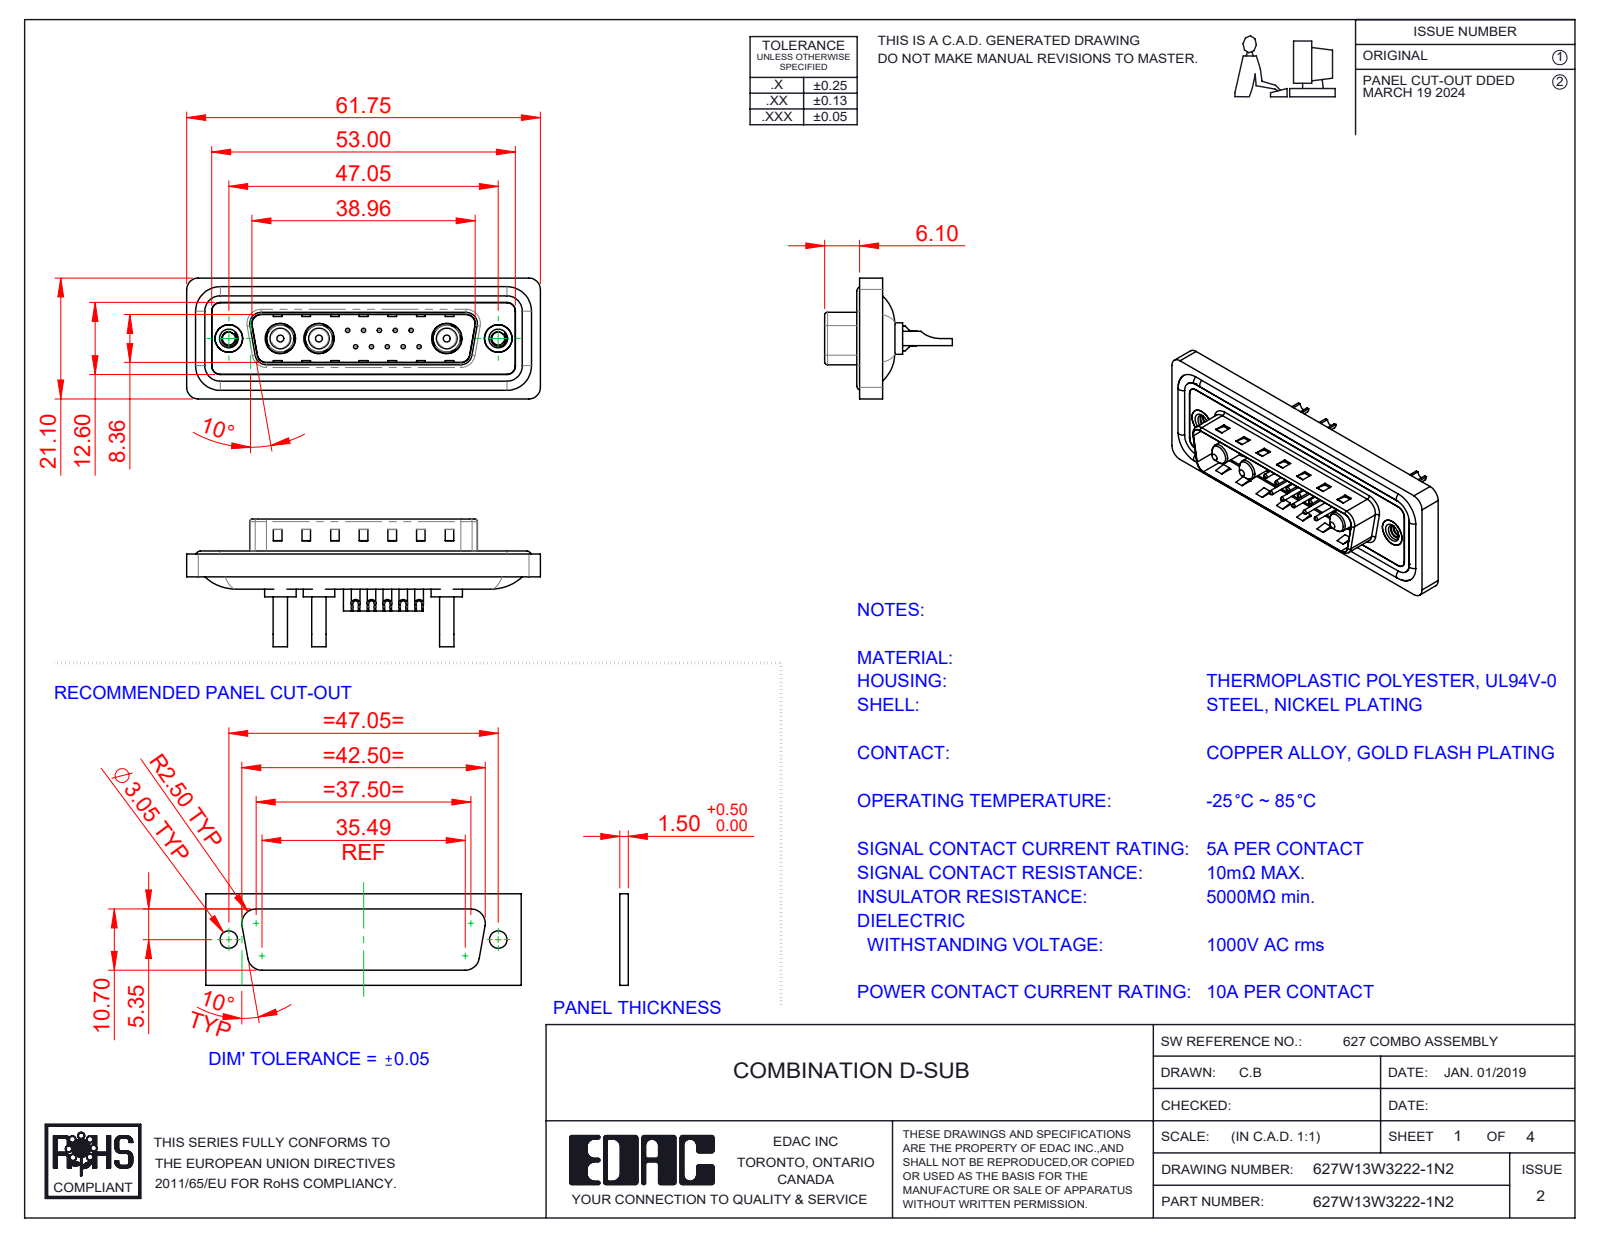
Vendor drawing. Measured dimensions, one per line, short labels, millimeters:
name: 627Combo Contact Row 2_22; 627Combo Shell Front_25 Contacts; 627Combo Waterproof Housing_25 Contacts; Power Pin_10A SC (+5 more)
written by: SolidWorks 2023 (CONFIG_CONTROL_DESIGN)
unit: mm
bodies: 23 solids, 988 faces (335 planar, 414 cylindrical, 239 other)
size: 61.75 × 22.3 × 21.1
volume: 7 342 mm³; area: 12 097 mm²
holes: 10× ⌀0.75, 10× ⌀1, 10× ⌀1.6, 10× ⌀2, 3× ⌀1.7, 3× ⌀4.85, 3× ⌀5.3, 2× ⌀2.26, 2× ⌀4, 2× ⌀4.8, 2× ⌀5
bosses: 10× ⌀1.5, 4× ⌀1.6, 3× ⌀5.5, 3× ⌀5.2, 3× ⌀4.75, 3× ⌀3.75, 3× ⌀3.6, 3× ⌀2.5
rounds: 22× R1.5, 18× R2, 8× R0.5, 8× R1.6, 6× R1, 4× R0.25, 4× R0.6, 4× R0.65
face distances: 0.4, 1.5, 1.1, 1.6, 0.5, 3.1, 2.9, 0.82, 9.58, 4.1
hole spacings: 3.16, 2.77, 5.04, 5.54, 7.49, 5.03, 8.31, 10.11
